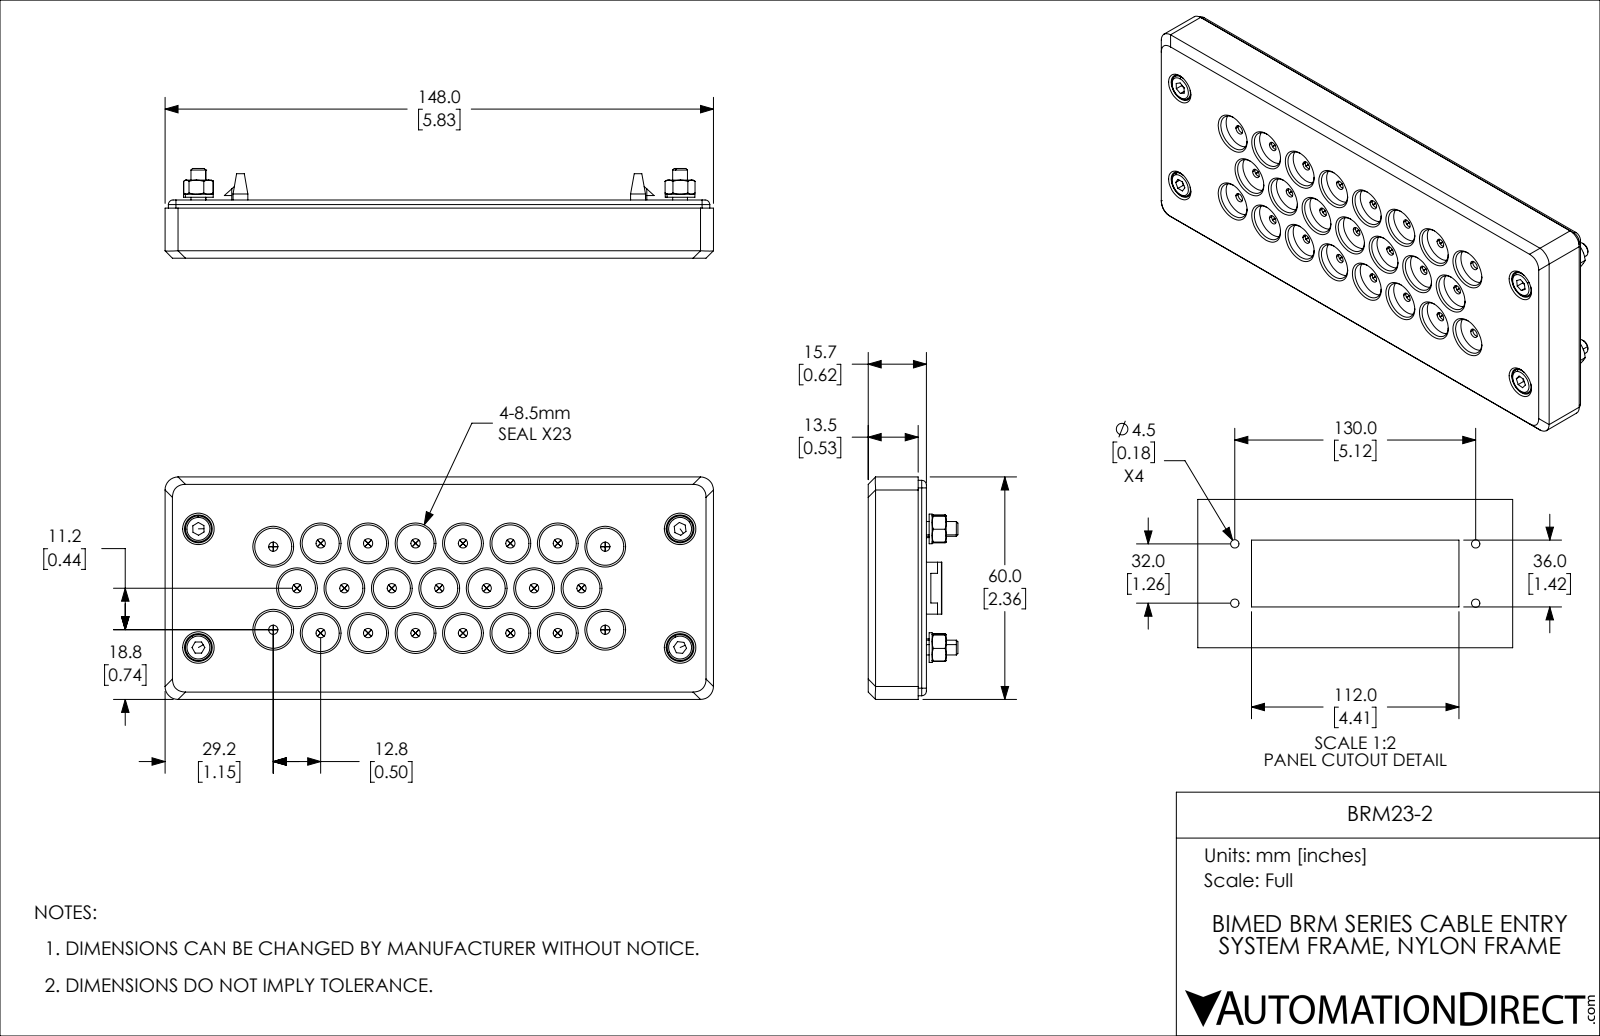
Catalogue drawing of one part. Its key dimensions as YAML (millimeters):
part_name: "BRM23-2"
step_written_by: "SolidWorks 2021 (CONFIG_CONTROL_DESIGN)"
units: millimeters
bodies: {solids: 18, faces: 1453, planar: 457, cylindrical: 688, other: 308}
overall_size: [148, 60, 24.2]
volume: 86814
surface_area: 90594
round_holes:
  - {diameter: 2.5, count: 27}
  - {diameter: 10, count: 23}
  - {diameter: 12, count: 23}
  - {diameter: 2.8, count: 20}
  - {diameter: 3.24, count: 4}
  - {diameter: 4.3, count: 4}
  - {diameter: 4.5, count: 4}
  - {diameter: 7.5, count: 4}
round_bosses_or_shafts:
  - {diameter: 2.5, count: 16}
  - {diameter: 4, count: 8}
  - {diameter: 8, count: 4}
  - {diameter: 7, count: 4}
partial_cylinders:
  - {radius: 1, count: 28}
  - {radius: 1.25, count: 8}
  - {radius: 5, count: 8}
  - {radius: 0.5, count: 6}
  - {radius: 2, count: 4}
  - {radius: 2.05, count: 4}
  - {radius: 3.5, count: 4}
  - {radius: 4.95, count: 4}
face_to_face_distances: [0.8, 2, 2.8, 5, 3, 5.8, 2.5, 8.3, 5.3, 3.3]
hole_center_spacings: [13.69, 22.69, 12.8, 34.21, 25.6, 46.41, 27.38, 38.4]
